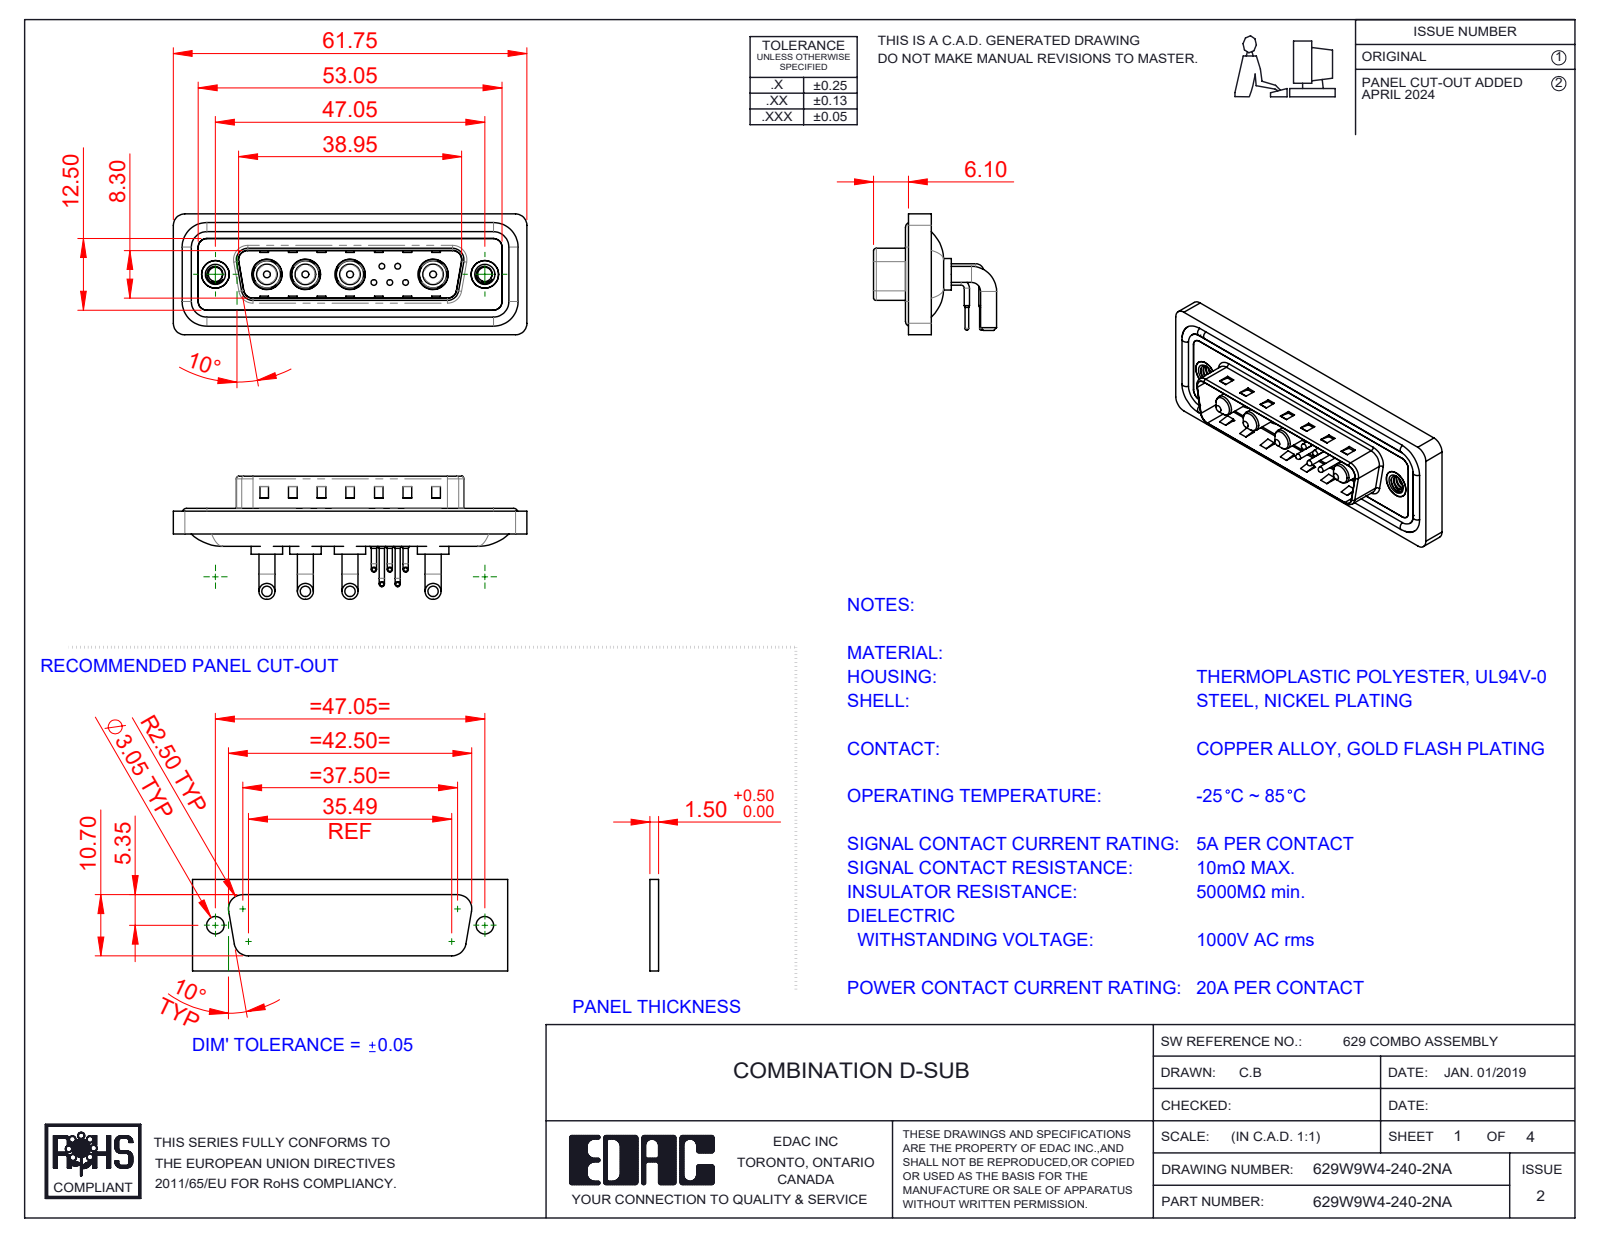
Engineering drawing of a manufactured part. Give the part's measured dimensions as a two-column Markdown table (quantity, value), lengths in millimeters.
| quantity | value |
| --- | --- |
| part name | 629Combo Housing_9W4; 629Combo Threaded Rivet_A; Power Pin_20A RA; 629Combo Shell Rear_25 Contacts (+5 more) |
| STEP written by | SolidWorks 2023 (CONFIG_CONTROL_DESIGN) |
| units | millimeters |
| bodies | 20 solids, 1199 faces (569 planar, 450 cylindrical, 180 other) |
| overall size | 61.75 × 21.5 × 21.1 |
| volume | 7 708 mm³ |
| surface area | 12 380 mm² |
| round holes (diameter × count) | 0.75 × 5, 1.6 × 5, 2 × 5, 4.85 × 4, 5.3 × 4, 2.5 × 2, 4 × 2, 4.8 × 2, 5 × 2 |
| round bosses / shafts (diameter × count) | 0.9 × 10, 2.8 × 8, 1.5 × 5, 1 × 5, 0.65 × 5, 5.5 × 4, 5.2 × 4, 4.75 × 4 |
| partial cylindrical surfaces (radius × count) | 1.5 × 18, 2 × 18, 0.5 × 8, 1.6 × 8, 1.01 × 5, 0.25 × 4, 0.6 × 4, 0.65 × 4 |
| main face-to-face distances | 0.4, 2.9, 0.8, 4.1, 1.1, 4.5, 2.1, 1.6, 1.5, 3.1 |
| hole center spacings | 3.16, 2.77, 5.04, 14.5, 2.78, 4.4, 4.41, 5 |
